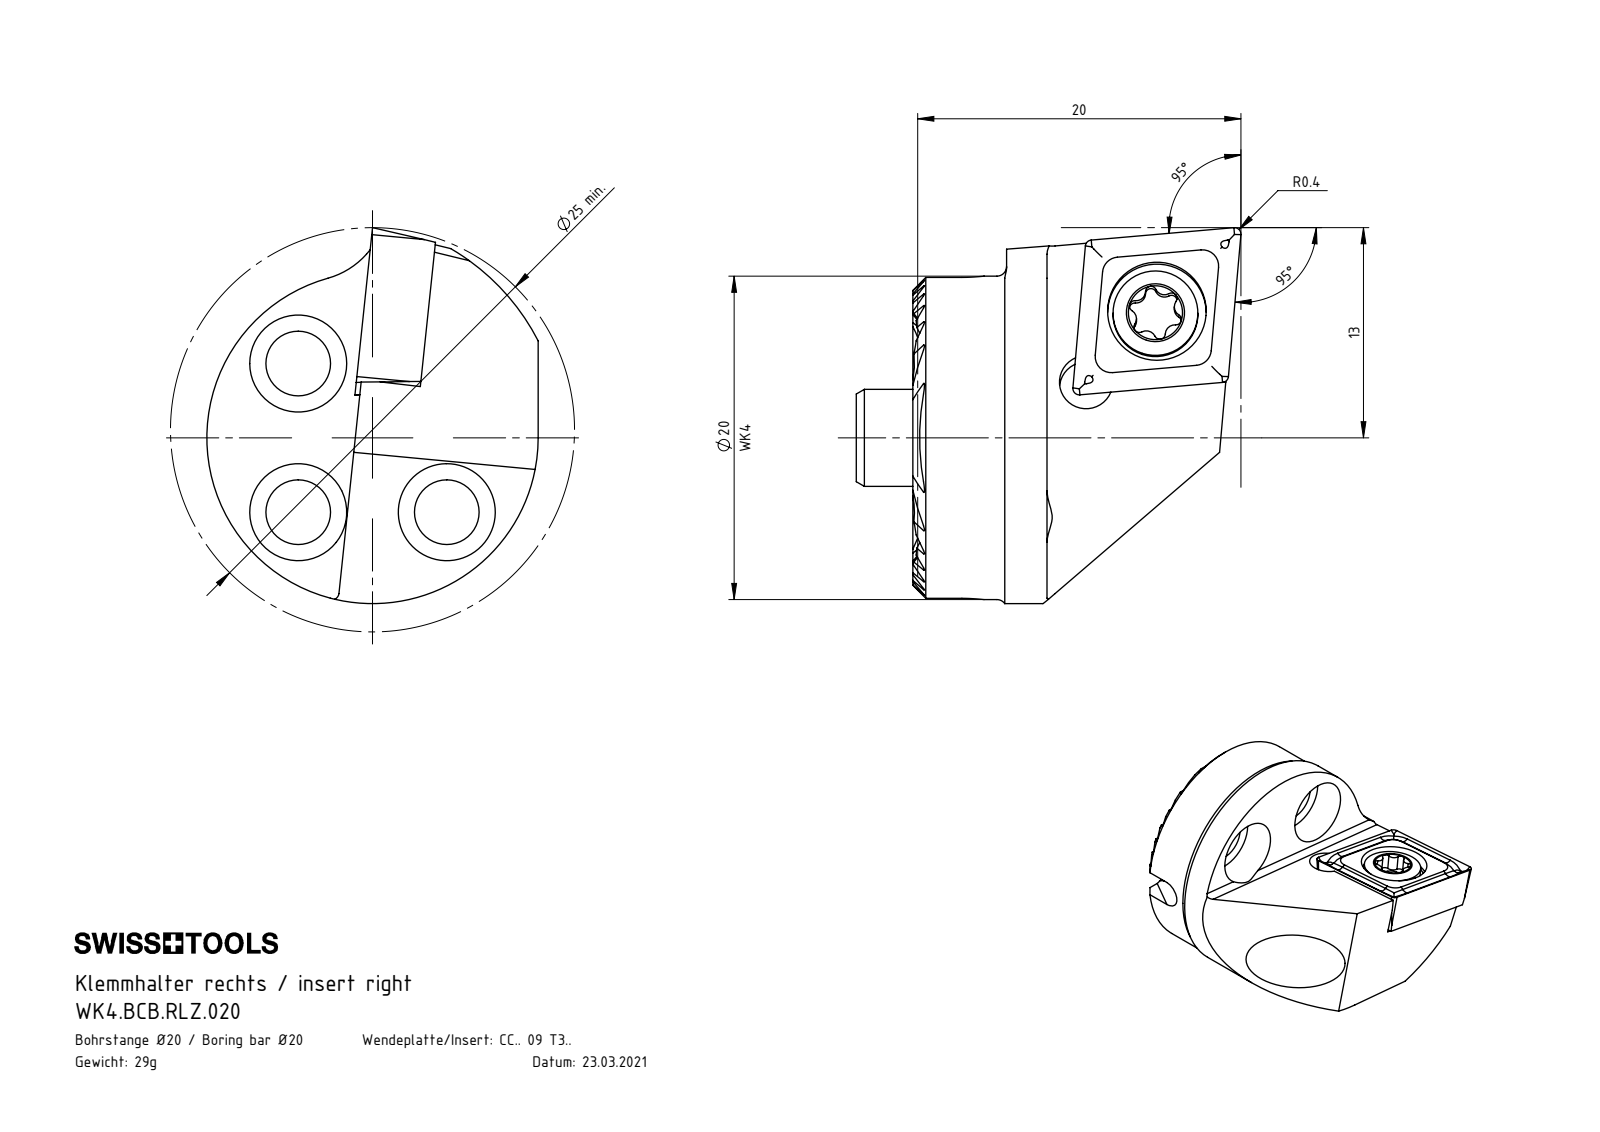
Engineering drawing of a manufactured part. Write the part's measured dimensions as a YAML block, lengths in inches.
part_name: "WK4.BCB.RLZ.020; CCMT09T304; WCB-ER2.001.009_A; WK4-BCB.RLZ.020_A (+1 more)"
step_written_by: "SolidWorks 2017 (AUTOMOTIVE_DESIGN)"
units: inches
bodies: {solids: 4, faces: 254, planar: 134, cylindrical: 65, other: 55}
overall_size: [0.937, 0.915, 0.807]
volume: 0.227
surface_area: 4.659
round_holes:
  - {diameter: 0.157, count: 3}
  - {diameter: 0.236, count: 3}
  - {diameter: 0.13, count: 2}
  - {diameter: 0.165, count: 1}
  - {diameter: 0.173, count: 1}
  - {diameter: 0.235, count: 1}
  - {diameter: 0.24, count: 1}
round_bosses_or_shafts:
  - {diameter: 0.787, count: 1}
  - {diameter: 0.236, count: 1}
  - {diameter: 0.207, count: 1}
  - {diameter: 0.157, count: 1}
partial_cylinders:
  - {radius: 0.005, count: 16}
  - {radius: 0.013, count: 6}
  - {radius: 0.023, count: 6}
  - {radius: 0.02, count: 1}
  - {radius: 0.197, count: 1}
  - {radius: 0.404, count: 1}
  - {radius: 0.551, count: 1}
face_to_face_distances: [0.17, 0.043, 0.128, 0.144, 0.085, 0.213, 0.341, 0.085, 0.118, 0.298]
hole_center_spacings: [0.256, 0.362, 0.239, 0.244, 0.512]
